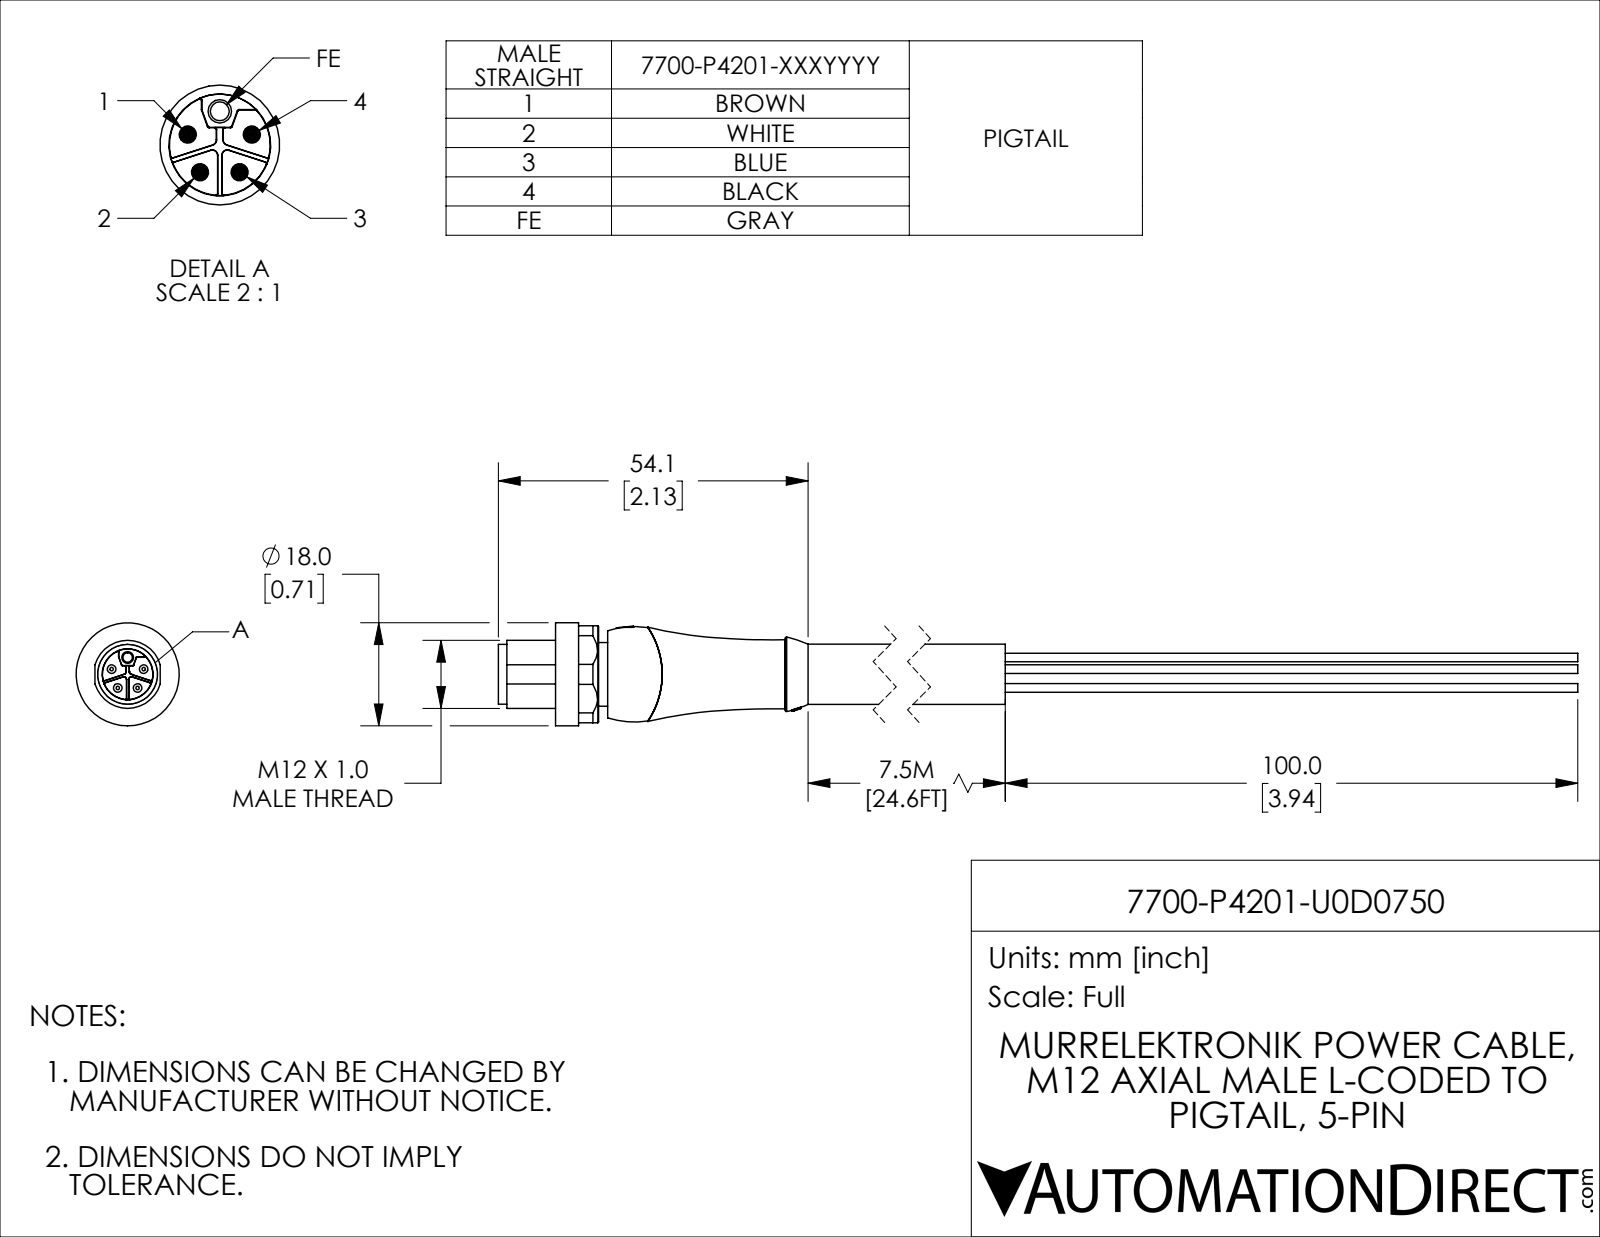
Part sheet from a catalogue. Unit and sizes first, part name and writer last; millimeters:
Units: millimetres
Overall size (bounding box): 254.1 × 18 × 18
Round holes (diameter × count): ⌀1.65 ×1
Round bosses / shafts (diameter × count): ⌀1.5 ×5, ⌀18 ×1, ⌀11.88 ×1, ⌀11.1 ×1, ⌀10.5 ×1, ⌀10.45 ×1
Partial cylindrical surfaces — rounded edges, fillets, slot ends (radius × count): R0.15 ×6, R1.13 ×1, R8.95 ×1
Main face-to-face distances: 9.1, 1.9, 7.2, 144.1, 136.9, 135, 16.94, 1.2, 8.4, 10.3
Volume: 17 489 mm³ · Surface area: 9 110 mm²
Bodies: 1 solid, 190 faces (87 planar, 51 cylindrical, 52 other)
Part name (STEP PRODUCT): 7700-P4201-U0D0750
STEP written by: SolidWorks 2021 (CONFIG_CONTROL_DESIGN)
